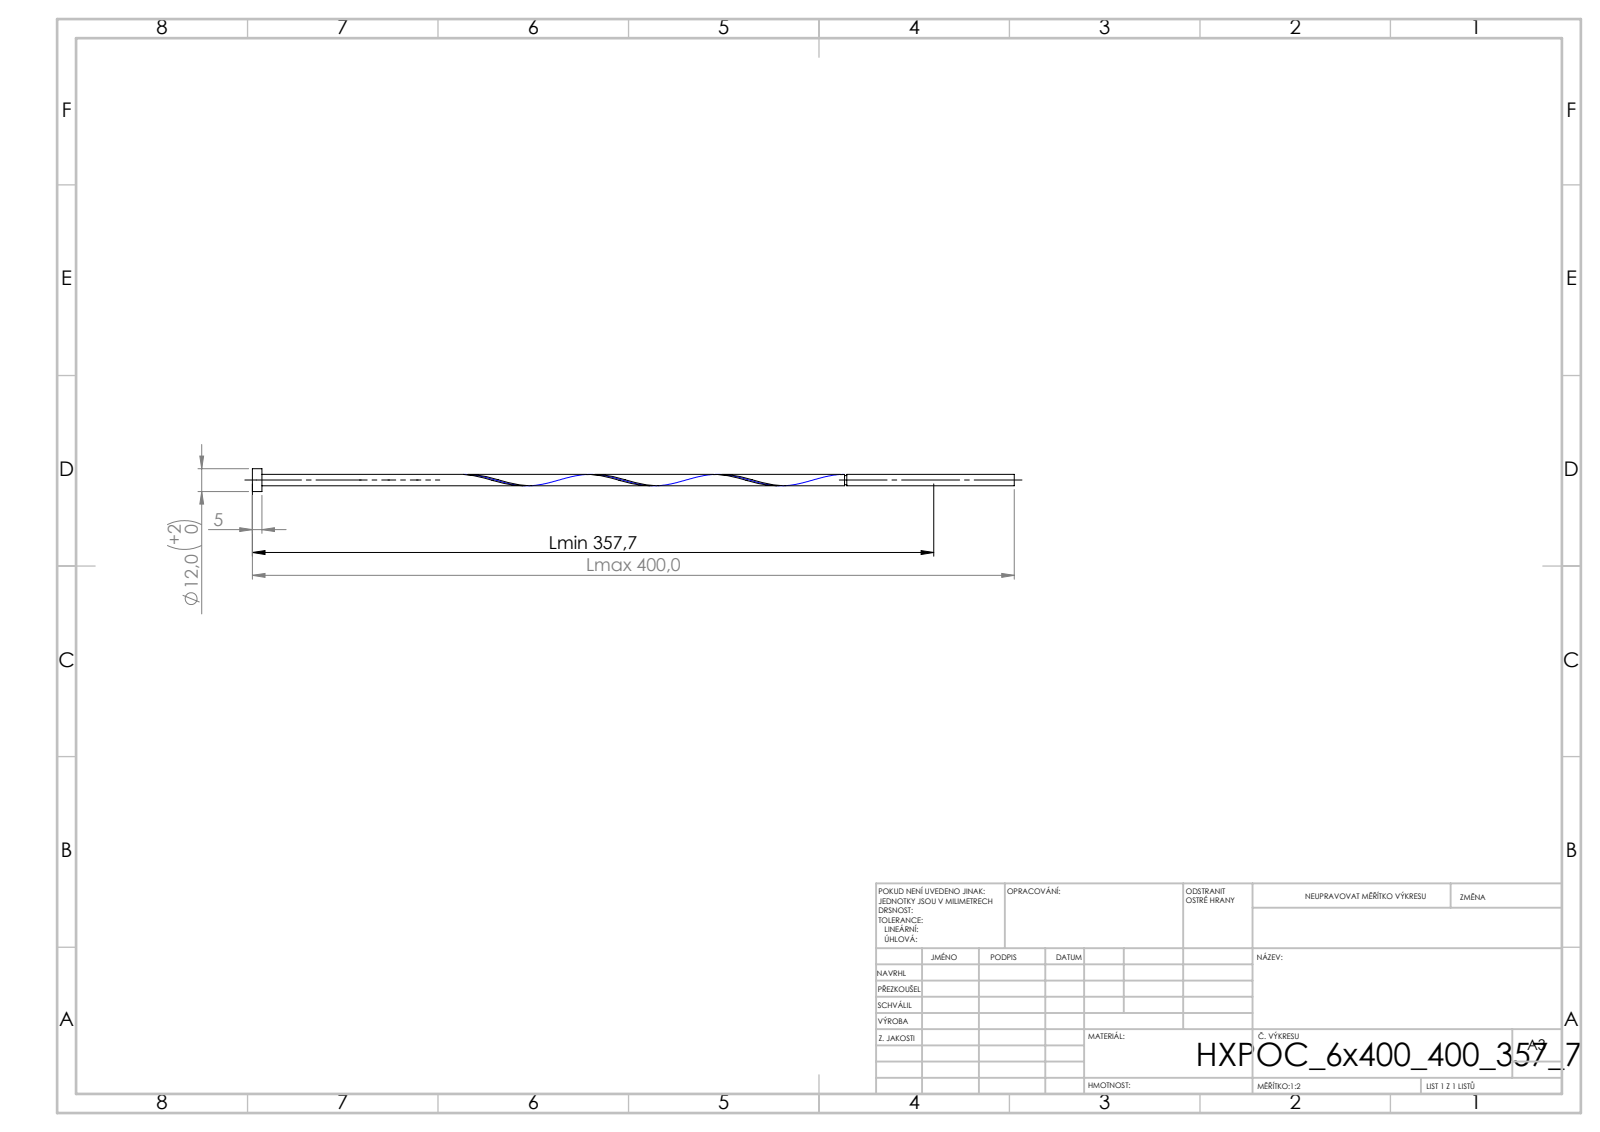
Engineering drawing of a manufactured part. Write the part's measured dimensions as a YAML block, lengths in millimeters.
step_written_by: "SolidWorks 2019 (CONFIG_CONTROL_DESIGN)"
units: millimeters
bodies: {solids: 1, faces: 16, planar: 6, cylindrical: 9, other: 1}
overall_size: [400, 12, 12]
volume: 14128
surface_area: 10510
round_bosses_or_shafts:
  - {diameter: 12, count: 1}
  - {diameter: 6, count: 1}
  - {diameter: 4.8, count: 1}
face_to_face_distances: [5, 400, 395, 312.09, 307.09, 87.91, 310.89, 305.89, 1.2, 89.11]
